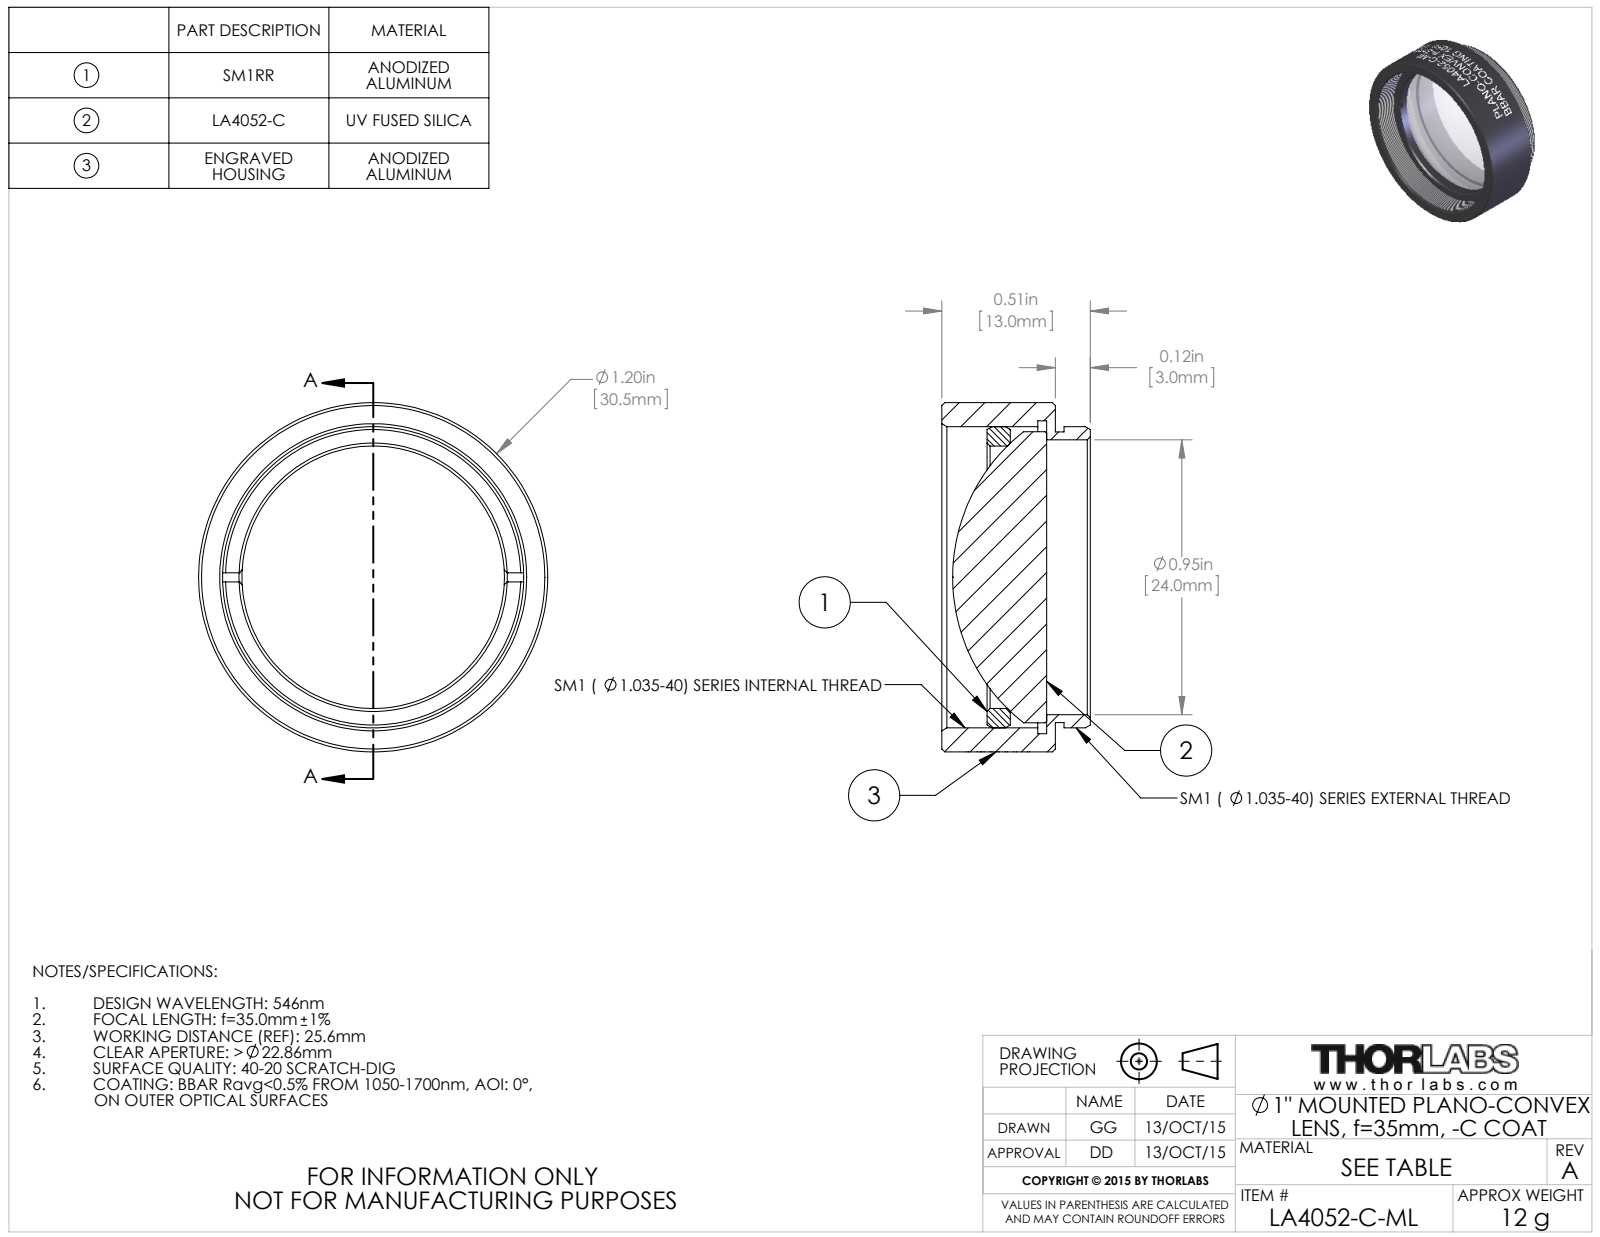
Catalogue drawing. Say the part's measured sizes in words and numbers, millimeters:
The part is named "TTN039129-E0W". Its 3-D file was written by "SolidWorks 2014 (CONFIG_CONTROL_DESIGN)". It is 3 solids with 152 faces: 20 planar, 106 cylindrical and 26 other. Overall it measures 30.48 by 30.48 by 12.95 millimeters. Its volume is 5 074 cubic millimeters and its surface area 4 698 square millimeters. Round holes: 1 of diameter 22.91, 1 of diameter 24, 1 of diameter 26.29, 1 of diameter 27.3. Round bosses or shafts: 1 of diameter 30.48, 1 of diameter 26.29, 1 of diameter 25.4, 1 of diameter 25.37. The main face-to-face distances are 0.76, 9.91, 9.15, 3.93, 3.17, 5.98, 5.96, 5.2, 2.03, 3.95.
